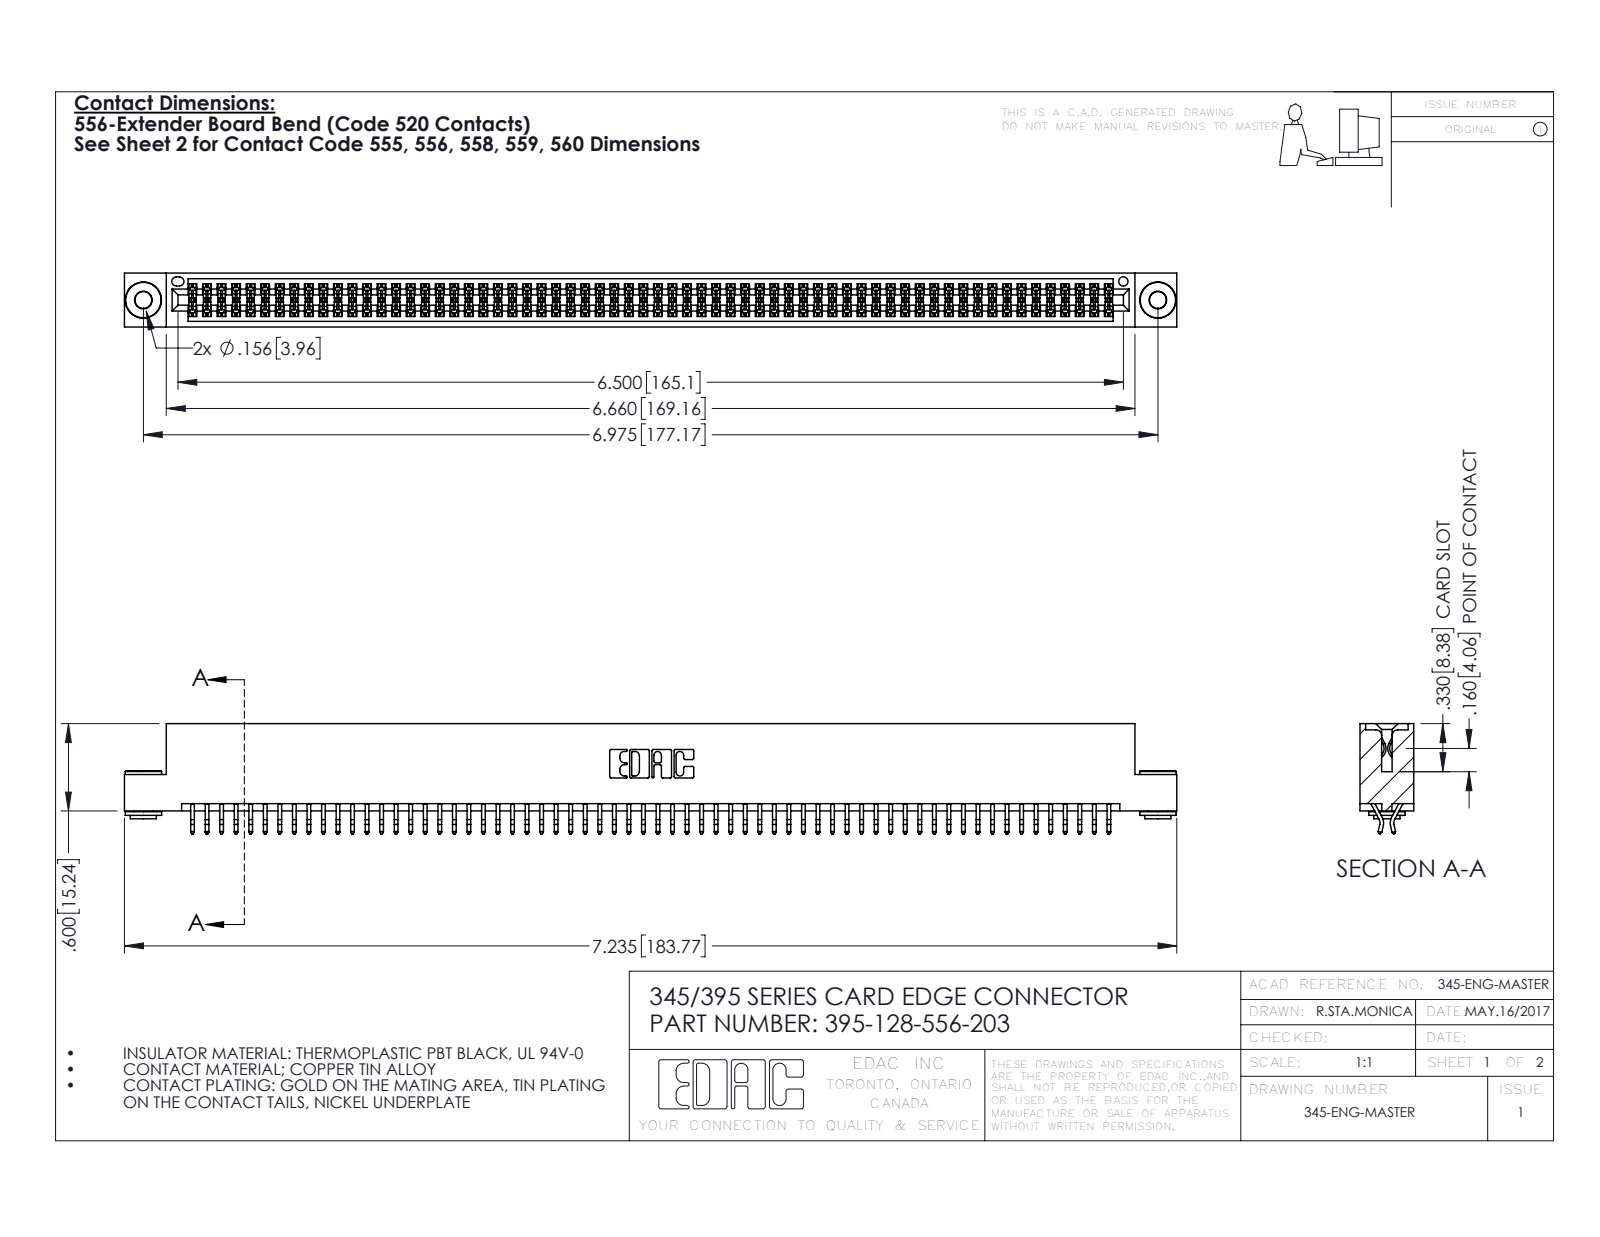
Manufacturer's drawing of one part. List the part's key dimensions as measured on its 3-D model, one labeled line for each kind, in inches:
Part name (STEP PRODUCT): 395-128-556-203; 345-250-002_345-250-002-102; 345-292-001_556 Tail; 345 Part_Flush Mounting Lugs - 0.156 Dia-TH
STEP written by: SolidWorks 2016 (CONFIG_CONTROL_DESIGN)
Units: inches
Bodies: 131 solids, 7332 faces (4826 planar, 2498 cylindrical, 8 other)
Overall size (bounding box): 7.235 × 0.757 × 0.37
Volume: 1.103 in³ · Surface area: 42.21 in²
Round holes (diameter × count): ⌀0.116 ×2, ⌀0.156 ×2, ⌀0.064 ×1
Round bosses / shafts (diameter × count): ⌀0.25 ×2, ⌀0.18 ×2, ⌀0.136 ×2
Partial cylindrical surfaces — rounded edges, fillets, slot ends (radius × count): R0.006 ×192, R0.01 ×22, R0.007 ×6, R0.031 ×6, R0.026 ×3, R0.01 ×2, R0.014 ×2, R0.019 ×2
Main face-to-face distances: 0.072, 0.298, 0.37, 0.2, 0.025, 0.098, 0.272, 0.225, 0.175, 0.149
Hole centre spacings: 0.27, 6.739, 6.975
